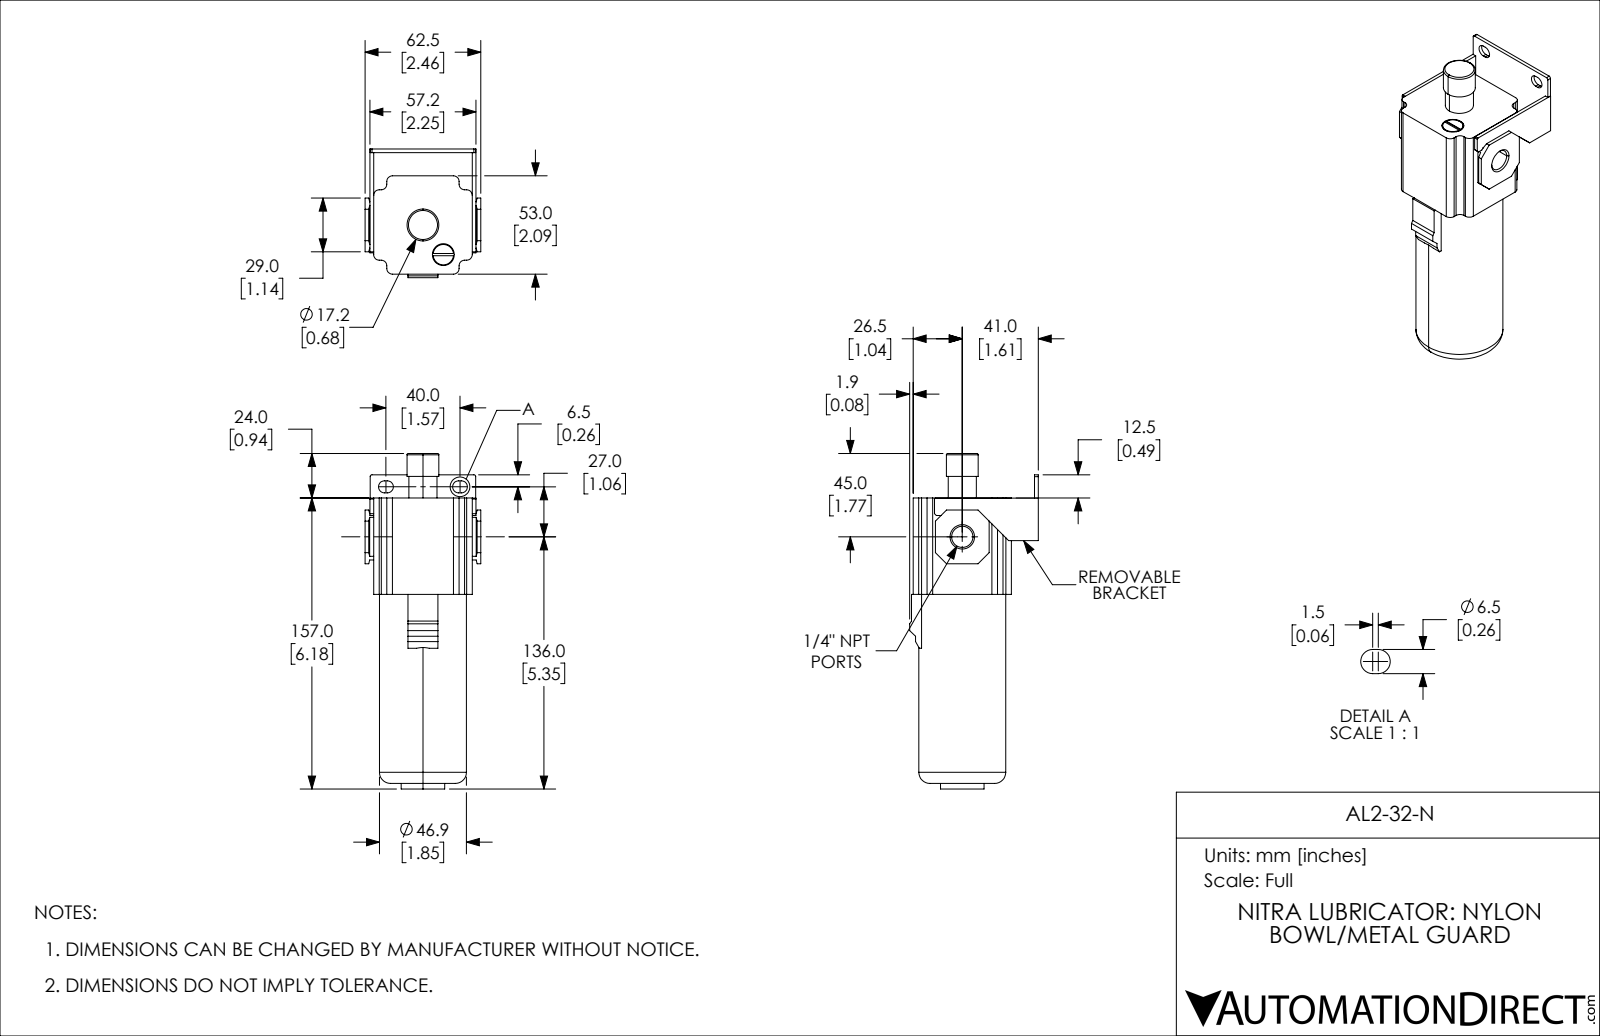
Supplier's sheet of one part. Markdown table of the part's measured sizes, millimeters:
| quantity | value |
| --- | --- |
| part name | AL2-32-N |
| STEP written by | SolidWorks 2019 (CONFIG_CONTROL_DESIGN) |
| units | millimeters |
| bodies | 1 solid, 138 faces (96 planar, 34 cylindrical, 8 other) |
| overall size | 181 × 69.42 × 62.5 |
| volume | 329 034 mm³ |
| surface area | 40 761 mm² |
| round holes (diameter × count) | 11.45 × 1, 11.8 × 1 |
| round bosses / shafts (diameter × count) | 46.9 × 1, 23.5 × 1, 17.2 × 1, 15.2 × 1, 11 × 1 |
| partial cylindrical surfaces (radius × count) | 3 × 12, 3.25 × 4, 1 × 2 |
| main face-to-face distances | 2, 12.5, 14.5, 67.5, 65.5, 53, 55.2, 2.65, 4.65, 57.85 |
